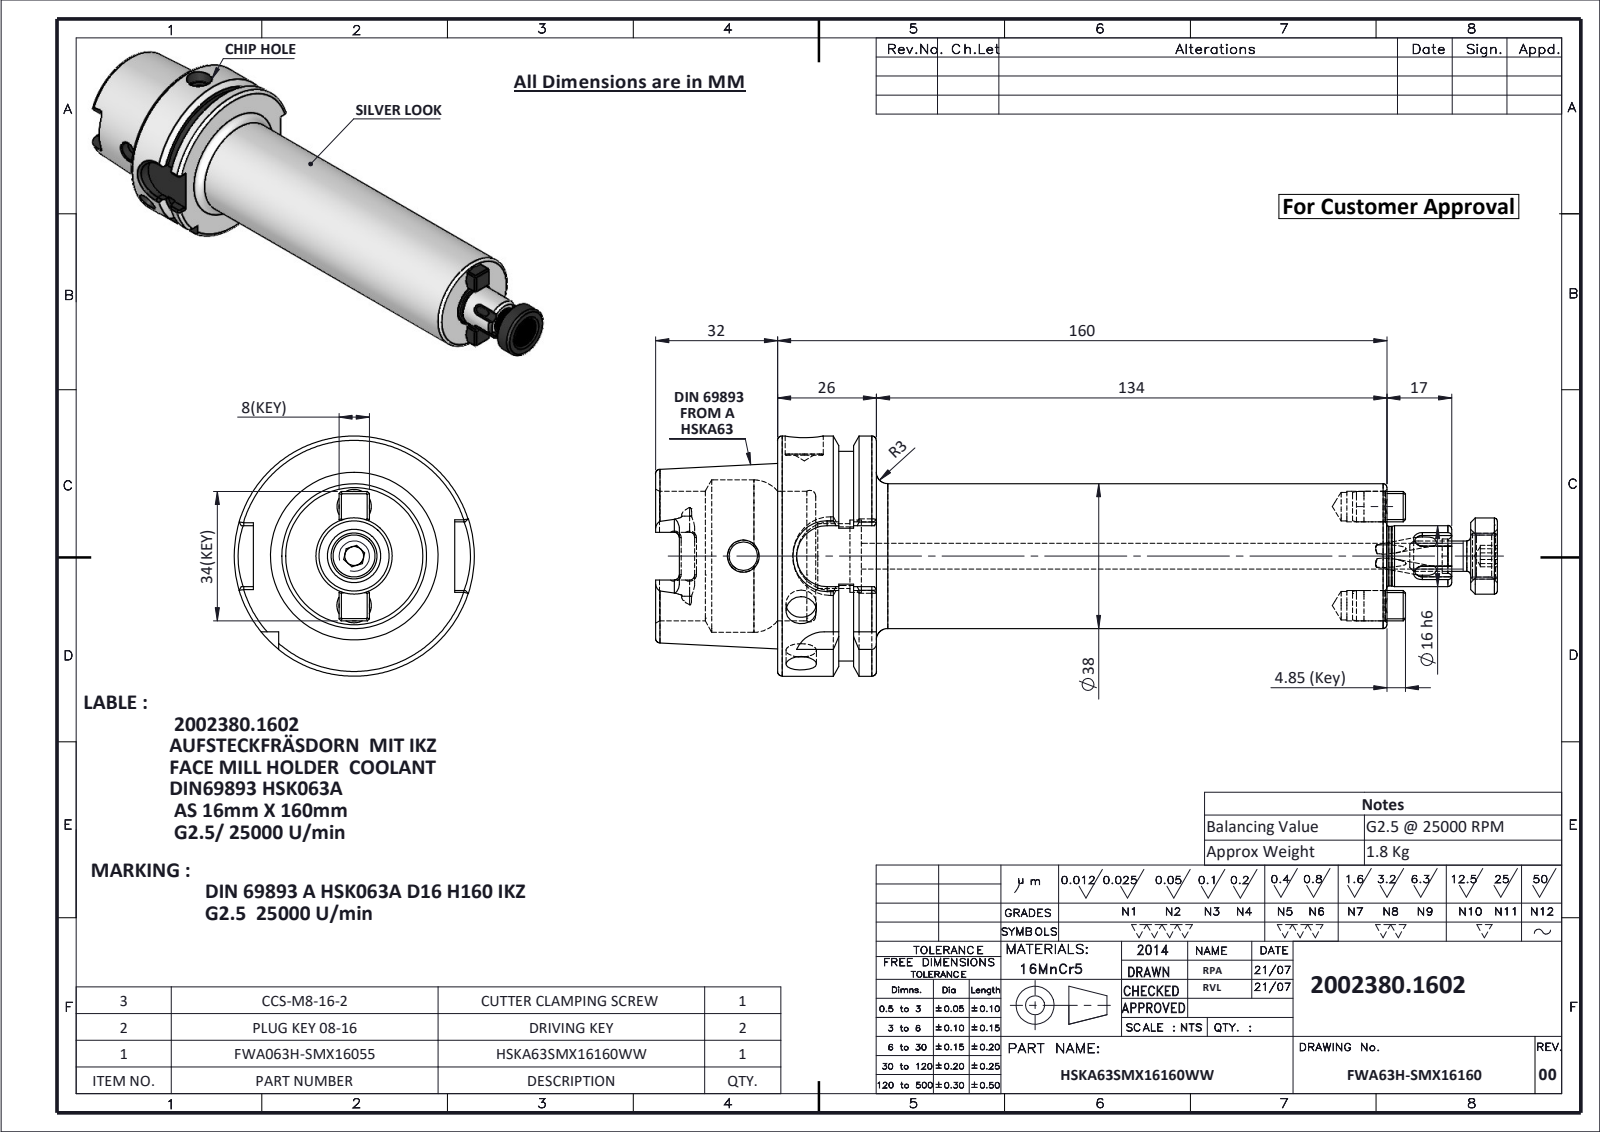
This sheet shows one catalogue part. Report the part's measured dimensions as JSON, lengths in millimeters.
{"part_name": "CCS-M8-16-2; HSKA63SMX16160WW; CCS-M8-16; PLUG KEY 08-16 (+2 more)", "step_written_by": "SolidWorks 2024 (CONFIG_CONTROL_DESIGN)", "units": "millimeters", "bodies": {"solids": 5, "faces": 352, "planar": 116, "cylindrical": 99, "other": 137}, "overall_size": [220.95, 63, 63], "volume_mm3": 233515, "surface_area_mm2": 46003, "round_holes": [[3, 4], [8, 4], [7.5, 3], [6.8, 1], [9, 1], [10, 1], [11, 1], [17, 1], [19, 1], [34, 1], [40, 1]], "round_bosses_or_shafts": [[8.02, 2], [7.98, 2], [63, 1], [55, 1], [38, 1], [20, 1], [16, 1], [15.6, 1]], "partial_cylinders_radius": [[1.3, 6], [2, 4], [2.88, 4], [5.25, 2], [8, 2], [9, 1]], "face_to_face_distances": [25.95, 159.95, 134, 10, 15.95, 149.95, 32, 42, 57.95, 191.95], "hole_center_spacings": [13, 26]}
